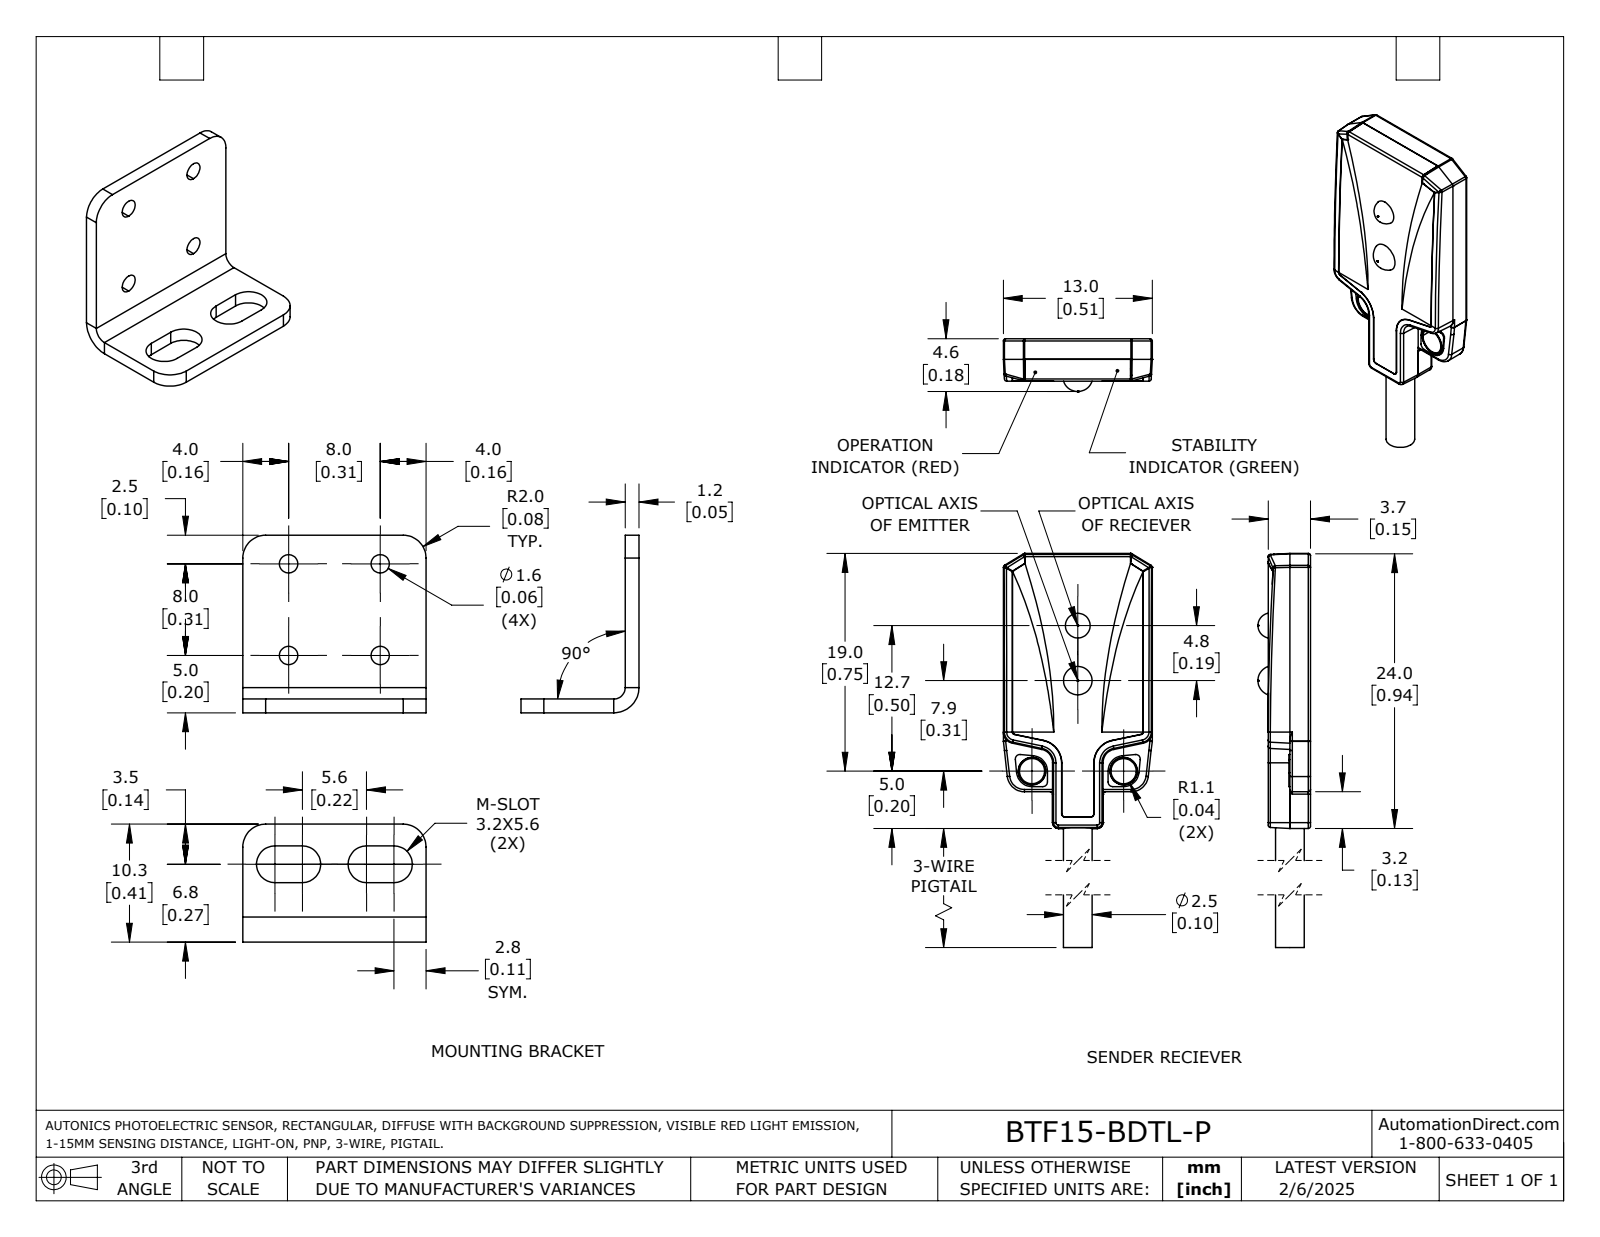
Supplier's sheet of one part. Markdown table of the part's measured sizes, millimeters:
| quantity | value |
| --- | --- |
| part name | BTF15-BDTL_BTF15-BDTL-P_BTF15-BDTD_BTF15-BDTD-P |
| STEP written by | SolidWorks 2024 (AUTOMOTIVE_DESIGN) |
| units | millimeters |
| bodies | 6 solids, 413 faces (175 planar, 126 cylindrical, 112 other) |
| overall size | 31.5 × 15.5 × 14.9 |
| volume | 1 446 mm³ |
| surface area | 1 936 mm² |
| round holes (diameter × count) | 1.6 × 4, 2.2 × 2, 2.4 × 2 |
| round bosses / shafts (diameter × count) | 3.6 × 2, 3.5 × 2, 2.36 × 2, 2 × 2, 2.5 × 1 |
| partial cylindrical surfaces (radius × count) | 0.2 × 41, 2 × 6, 0.4 × 4, 1.6 × 4, 1 × 3, 0.22 × 2, 0.3 × 2, 0.32 × 2 |
| main face-to-face distances | 1.2, 3.7, 4.9, 2.5, 1.9, 14.3, 15.5, 1.8, 1.3, 12.2 |
| hole center spacings | 8, 11.31 |
